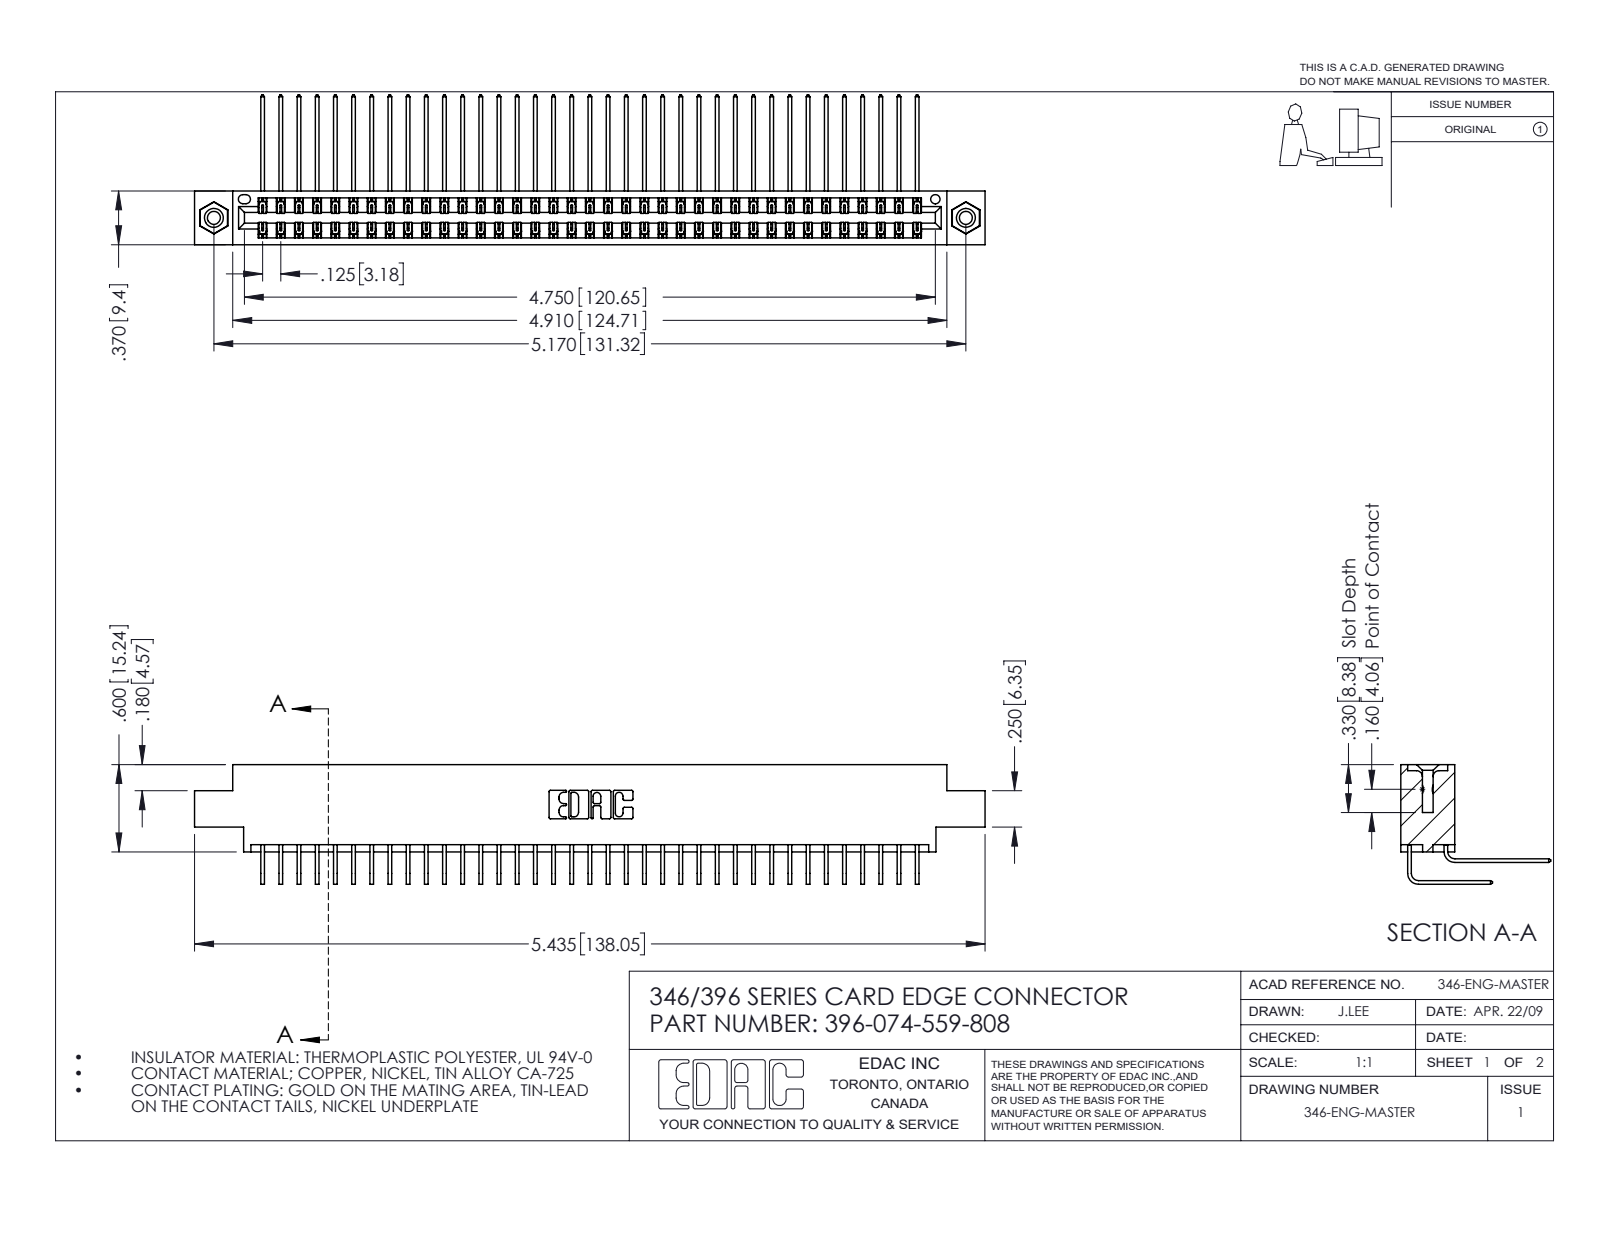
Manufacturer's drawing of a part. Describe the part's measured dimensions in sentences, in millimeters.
The part is named "346 Part_0.170 Offset - 0.156 Dia-TI; 345-292-001_559 Tail - 2; 345-292-001_558 559 Tail - 1; 345-250-001_345-250-003-102 (+1 more)". Its 3-D file was written by "SolidWorks 2016 (CONFIG_CONTROL_DESIGN)". It is 77 solids with 4182 faces: 2850 planar, 1316 cylindrical and 16 other. Overall it measures 138 by 26.2 by 20.9 millimeters. Its volume is 13 700 cubic millimeters and its surface area 20 990 square millimeters. Round holes: 2 of diameter 2.3, 2 of diameter 3.2, 2 of diameter 4, 1 of diameter 1.6. Round bosses or shafts: 2 of diameter 3.9. Partial cylindrical surfaces (rounded edges, fillets, slot ends): 111 of radius 0.2, 22 of radius 0.3, 6 of radius 0.2, 6 of radius 0.8, 3 of radius 0.7, 2 of radius 0.4, 2 of radius 0.6, 2 of radius 0.6. The main face-to-face distances are 1.2, 8.2, 0.6, 9.4, 6.4, 1.8, 7.6, 7, 5.6, 3.8. The hole center spacings are 6.2, 126, 131.3.
